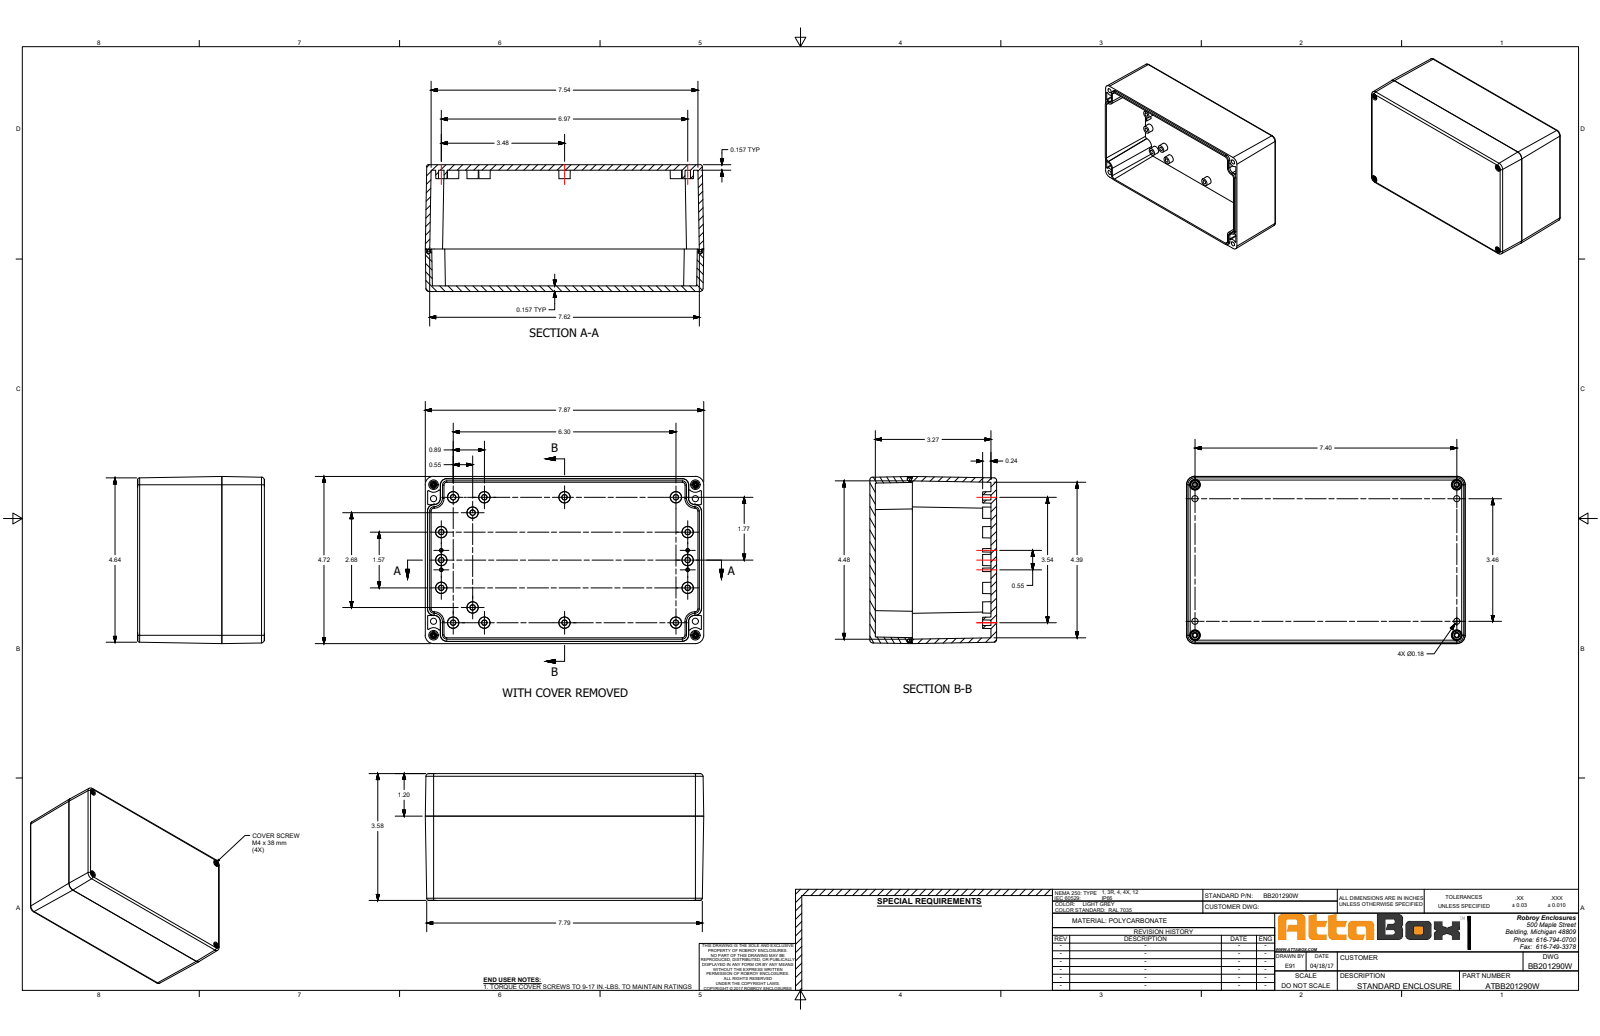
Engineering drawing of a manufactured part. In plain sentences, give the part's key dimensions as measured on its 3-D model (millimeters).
The part is named "BB201290W". Its 3-D file was written by "SolidWorks 2018 (AUTOMOTIVE_DESIGN)". It is 11 solids with 1691 faces: 631 planar, 436 cylindrical and 624 other. Overall it measures 200 by 120 by 91 millimeters. Its volume is 392 500 cubic millimeters and its surface area 238 100 square millimeters. Round holes: 4 of diameter 3.3, 4 of diameter 4.5, 4 of diameter 4.8, 4 of diameter 5.1, 4 of diameter 6, 4 of diameter 7, 4 of diameter 7.4, 4 of diameter 7.8. Round bosses or shafts: 4 of diameter 6.8, 4 of diameter 4.4, 4 of diameter 4, 4 of diameter 3.3. Partial cylindrical surfaces (rounded edges, fillets, slot ends): 48 of radius 1, 38 of radius 0.5, 12 of radius 5, 8 of radius 2.5, 4 of radius 1.5, 4 of radius 2, 4 of radius 2.6, 4 of radius 3. The main face-to-face distances are 4, 87, 3.2, 91, 83, 120, 116.8, 4.3, 115.7, 112.5. The hole center spacings are 10, 98, 188, 188.3, 212, 88, 108, 207.6.
